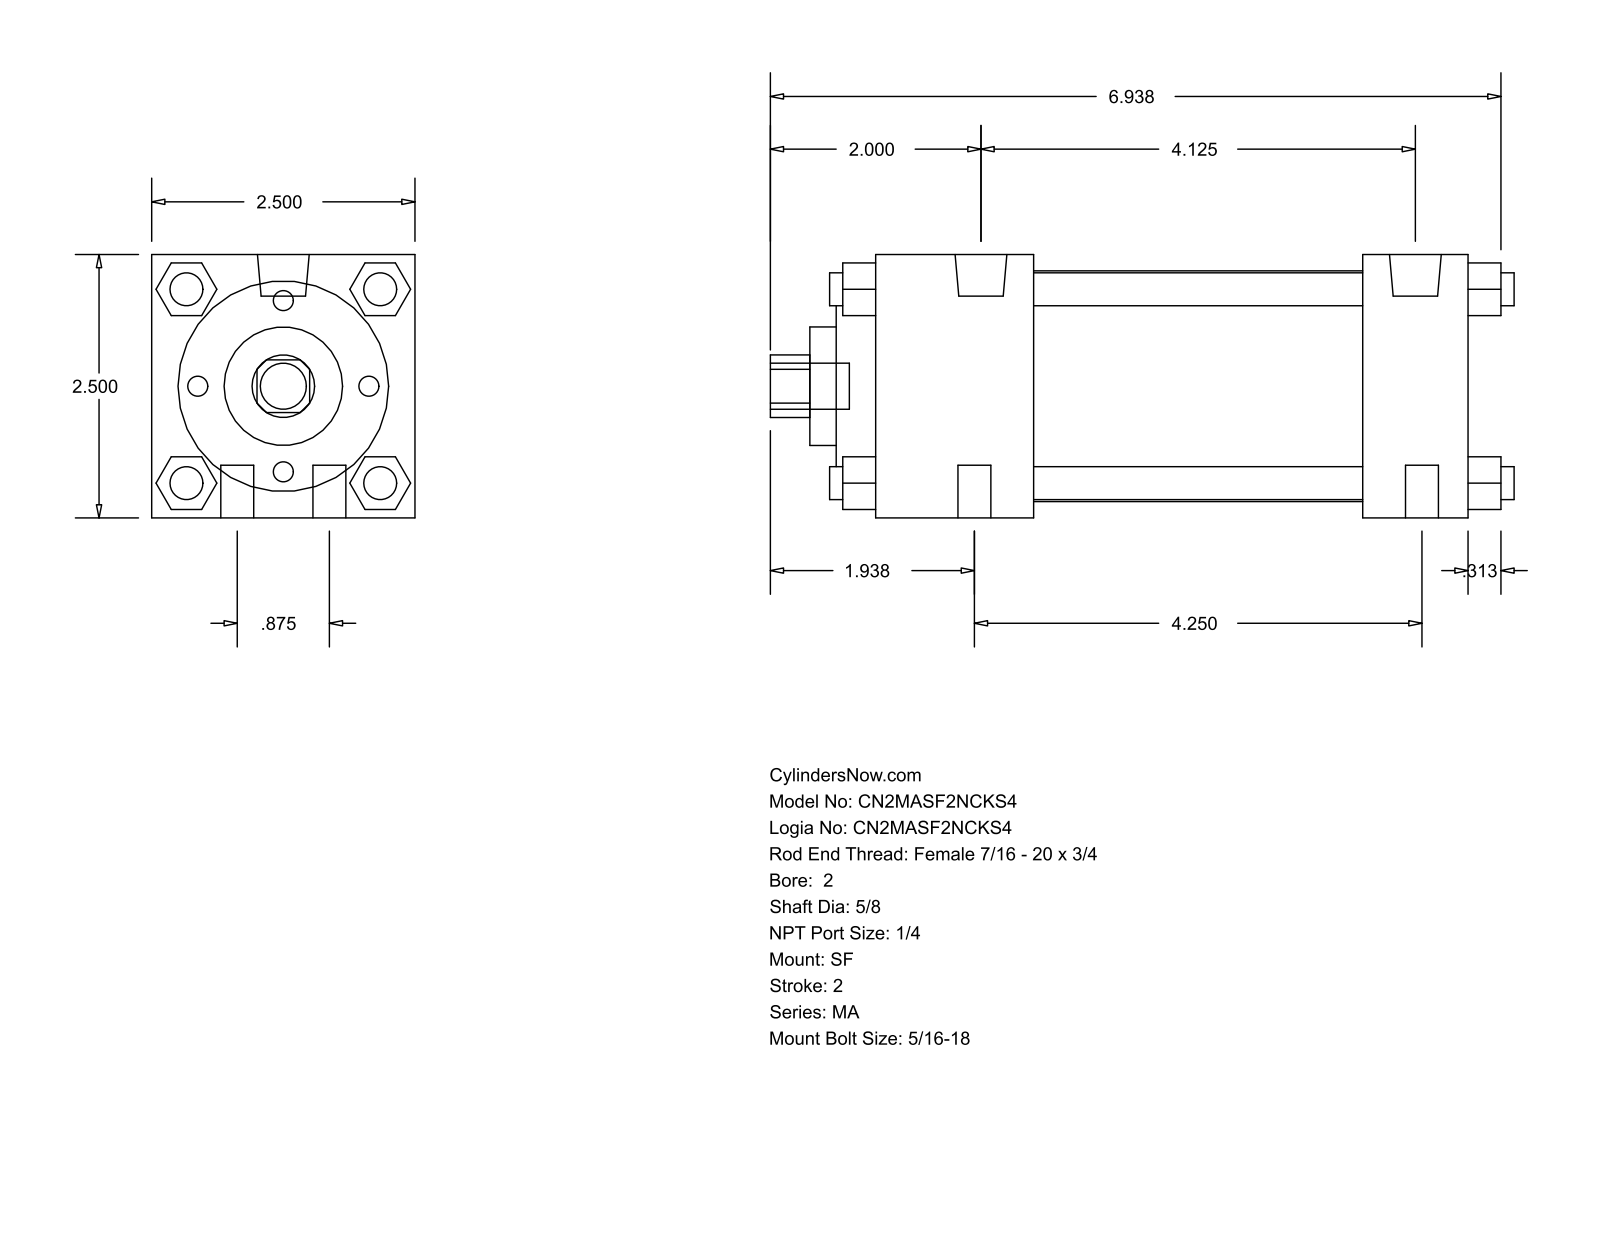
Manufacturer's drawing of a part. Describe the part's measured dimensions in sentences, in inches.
The part is named "MA_SF__0200_0.625". Its 3-D file was written by "GSSL Pune (CONFIG_CONTROL_DESIGN)". It is 0 solids with 126 faces: 95 planar, 31 cylindrical and 0 other. Overall it measures 7.063 by 2.5 by 2.5 inches. Round holes: 1 of diameter 0.625, 1 of diameter 1.125, 1 of diameter 2, 1 of diameter 2.19. Round bosses or shafts: 10 of diameter 0.313, 2 of diameter 0.492, 1 of diameter 0.437. Partial cylindrical surfaces (rounded edges, fillets, slot ends): 1 of radius 0.297. The main face-to-face distances are 2.5, 0.5, 1, 1.5, 5.625, 0.375, 4.625, 3.125, 4.125, 1.875.
